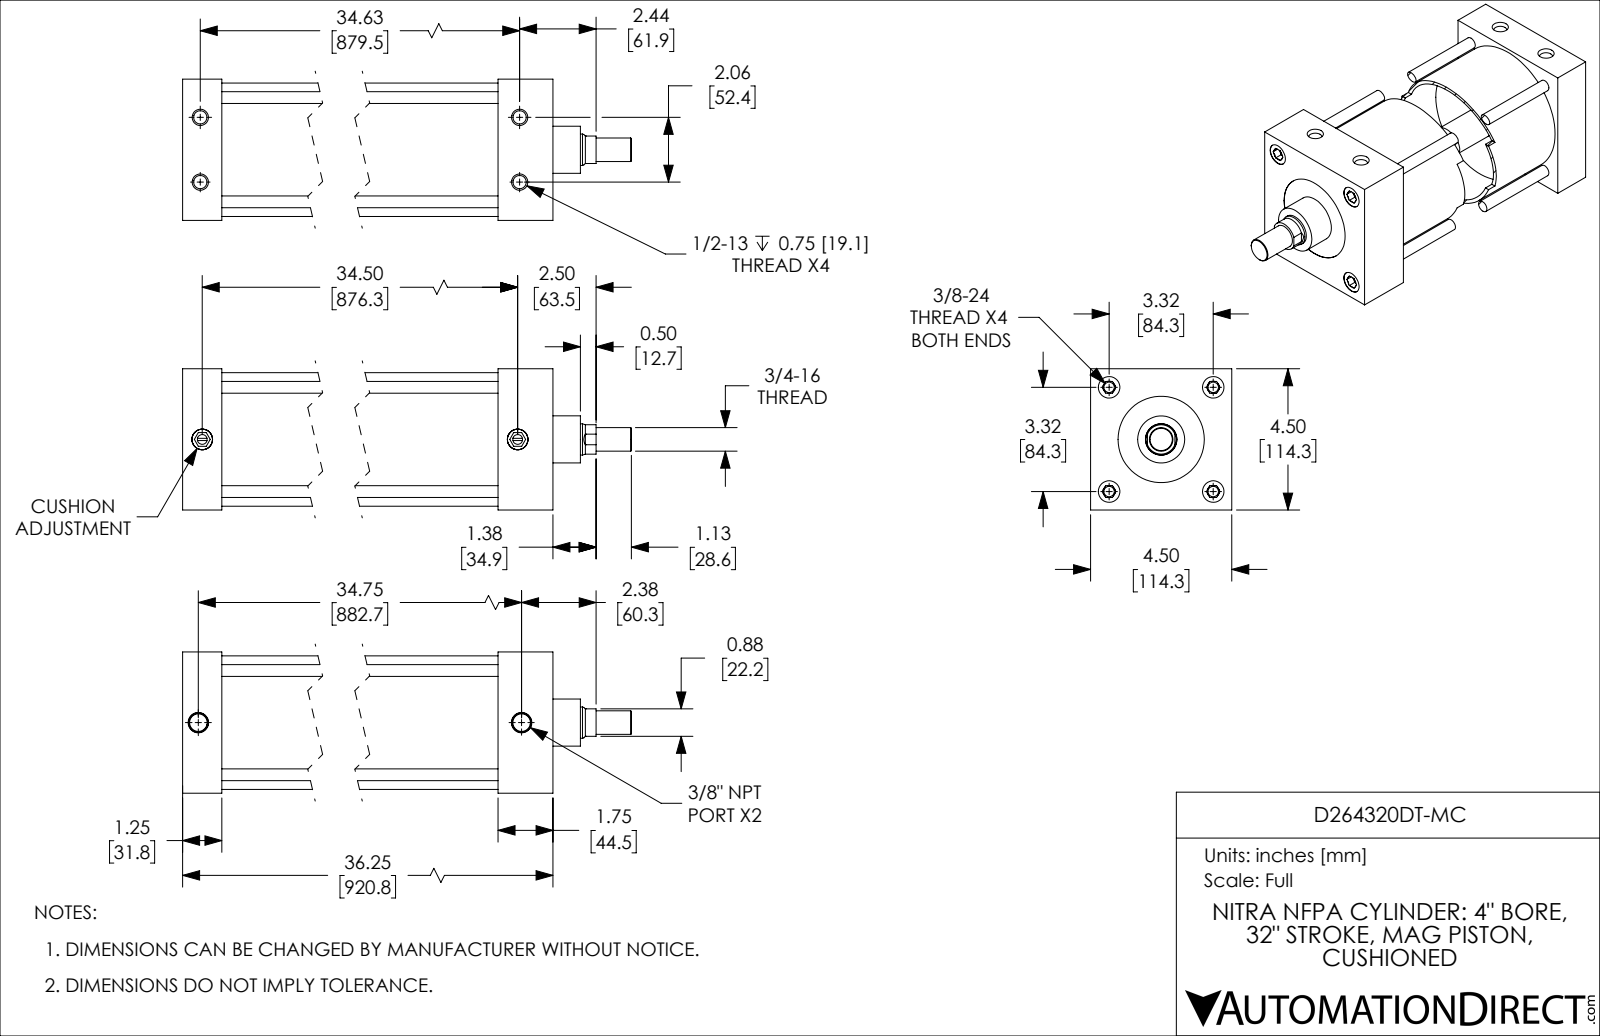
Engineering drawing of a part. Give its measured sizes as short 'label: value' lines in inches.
name: D264320DT-MC; D264320DT-MC_CUSHION; D264320DT-MC_PISTON_KK1; D264320DT-MC_BODY
written by: SolidWorks 2019 (CONFIG_CONTROL_DESIGN)
unit: in
bodies: 4 solids, 246 faces (90 planar, 78 cylindrical, 78 other)
size: 38.75 × 4.5 × 4.5
volume: 170 in³; area: 1 338 in²
holes: 4× ⌀0.332, 4× ⌀0.422, 4× ⌀0.687, 2× ⌀0.312, 2× ⌀0.562, 2× ⌀0.656, 1× ⌀1.001, 1× ⌀2.75, 1× ⌀4.001
bosses: 4× ⌀0.375, 2× ⌀0.657, 1× ⌀4.251, 1× ⌀3.999, 1× ⌀1.5, 1× ⌀0.999, 1× ⌀0.75
rounds: 1× R0.469
face distances: 1.25, 4.5, 34.5, 33.25, 36.25, 35, 1.75, 2.5, 32, 33.75
hole spacings: 1.033, 2.347, 3.32, 34.703, 2.062, 4.695, 34.625, 34.686
